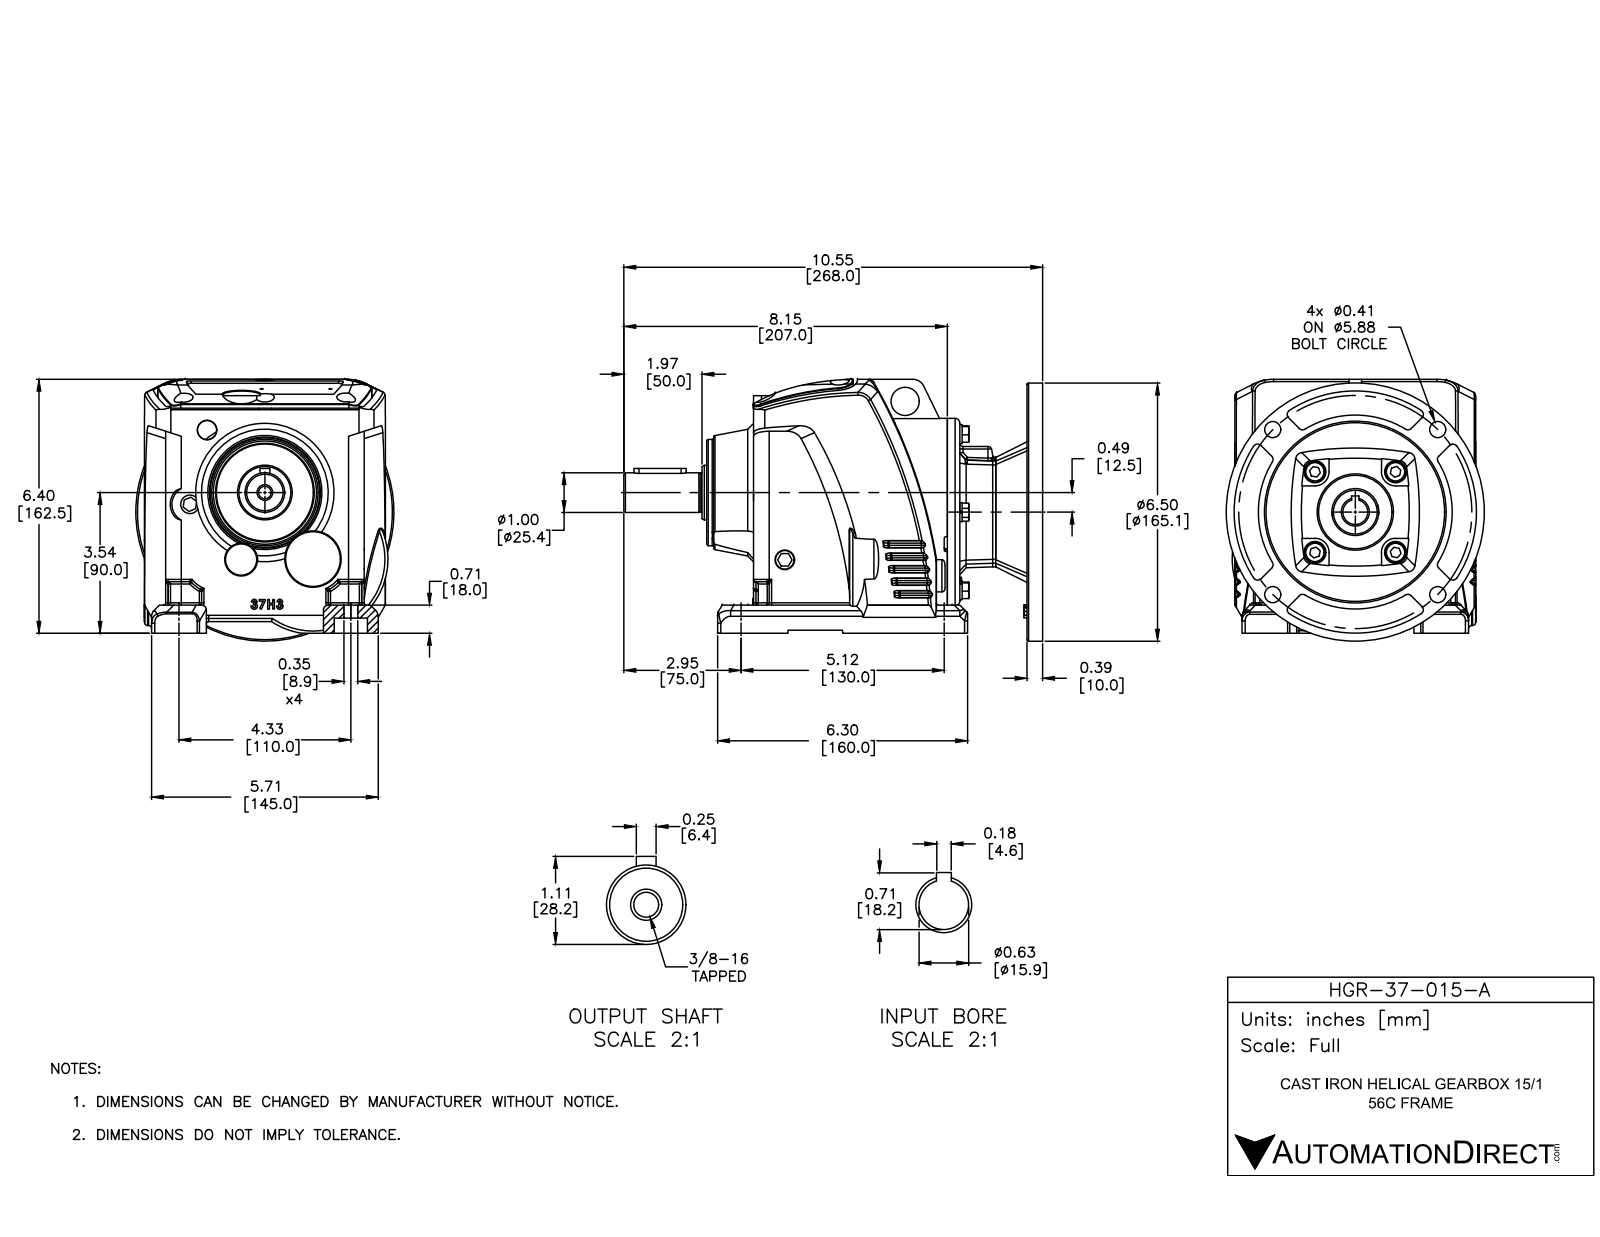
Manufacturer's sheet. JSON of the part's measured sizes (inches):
{"part_name": "HGR-37-015-A", "step_written_by": "SolidWorks 2015 (AUTOMOTIVE_DESIGN)", "units": "inches", "bodies": {"solids": 4, "faces": 1036, "planar": 343, "cylindrical": 277, "other": 416}, "overall_size": [10.551, 6.596, 6.5], "volume_in3": 169.7, "surface_area_in2": 383.8, "round_holes": [[0.472, 6], [0.406, 4], [0.55, 4], [0.276, 3], [0.079, 2], [0.354, 2], [0.394, 2], [0.313, 1], [0.625, 1], [0.709, 1], [0.945, 1], [1.181, 1]], "round_bosses_or_shafts": [[0.512, 4], [0.48, 4], [0.315, 4], [1.378, 2], [0.472, 2], [6.5, 1], [4.724, 1], [2.677, 1]], "partial_cylinders_radius": [[0.059, 43], [0.118, 21], [0.079, 18], [0.197, 8], [0.354, 6], [0.394, 6], [0.315, 5], [0.276, 4]], "face_to_face_distances": [7.126, 0.236, 0.276, 0.394, 6.89, 1.102, 4.331, 0.157, 2.087, 0.079], "hole_center_spacings": [3.27, 1.437, 1.5, 2.032, 2.937, 4.154, 4.374, 1.143]}
